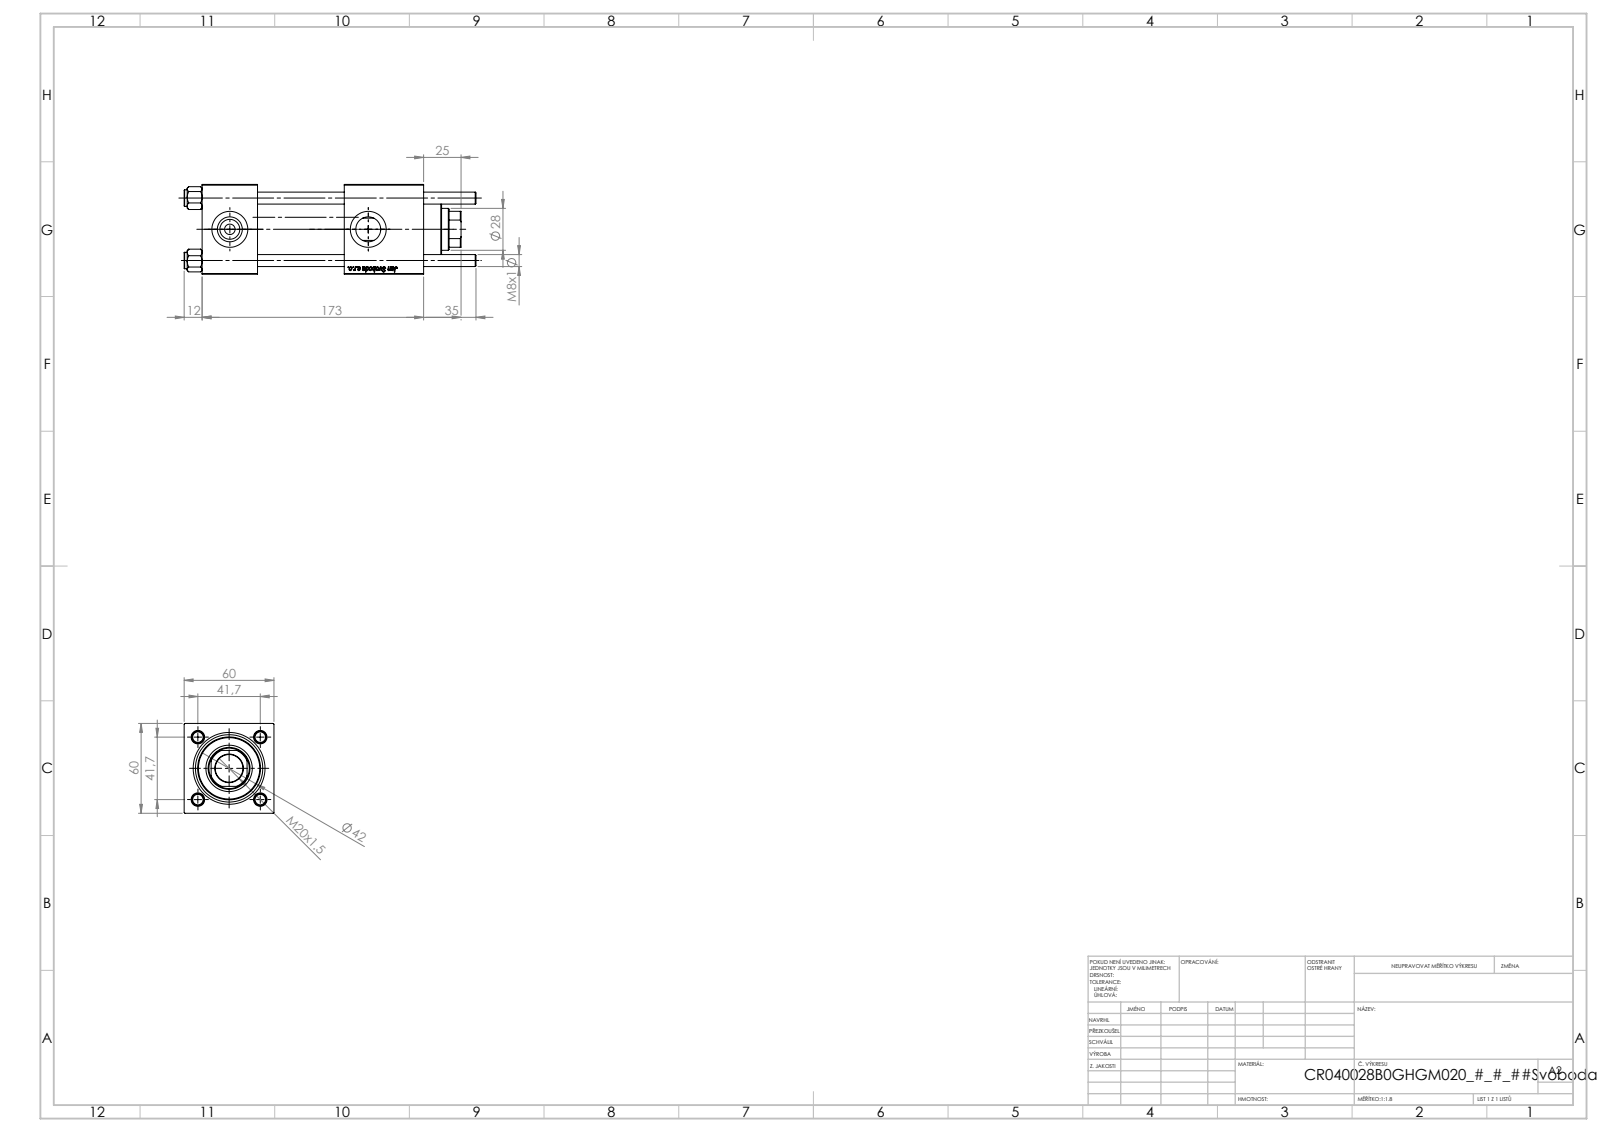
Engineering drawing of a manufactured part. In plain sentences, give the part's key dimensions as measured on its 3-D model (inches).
The part is named "V215CR_VCP_B; V215CR_B_TYCINKA; NUT_M5_B; V215_VC_A (+1 more)". Its 3-D file was written by "SolidWorks 2019 (CONFIG_CONTROL_DESIGN)". It is 11 solids with 1159 faces: 433 planar, 78 cylindrical and 648 other. Overall it measures 7.677 by 2.362 by 2.362 inches. Its volume is 26.58 cubic inches and its surface area 185.8 square inches. Round holes: 4 of diameter 0.315, 2 of diameter 0.276, 2 of diameter 0.656, 2 of diameter 0.945, 1 of diameter 0.728, 1 of diameter 1.102, 1 of diameter 1.22, 1 of diameter 1.575, 1 of diameter 1.772. Round bosses or shafts: 4 of diameter 0.433, 1 of diameter 1.811, 1 of diameter 1.654. Partial cylindrical surfaces (rounded edges, fillets, slot ends): 1 of radius 0.531. The main face-to-face distances are 2.362, 1.457, 2.283, 3.74, 4.697, 3.24, 0.957, 2.087, 5.827, 4.37. The hole center spacings are 1.161, 1.642, 2.322, 3.642.
